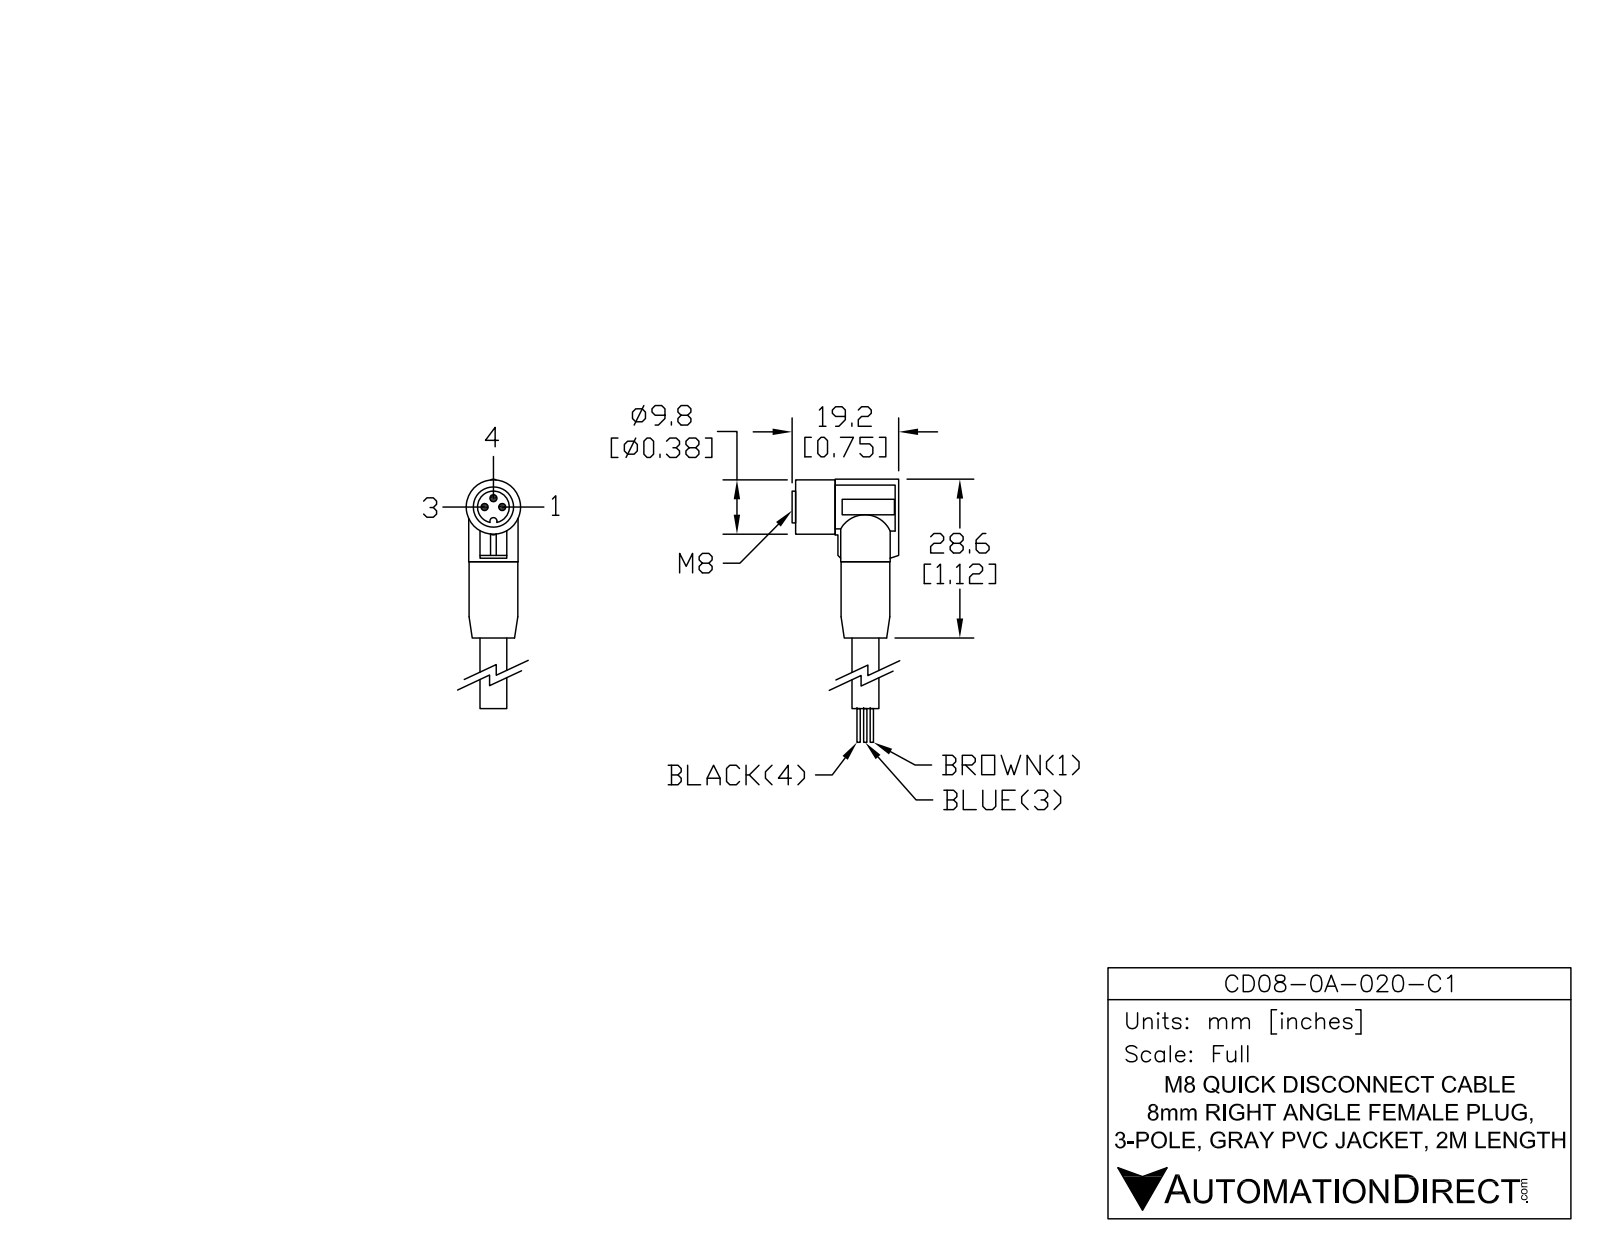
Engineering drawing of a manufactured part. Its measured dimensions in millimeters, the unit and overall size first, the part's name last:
Units: millimetres
Overall size (bounding box): 128.6 × 19.1 × 10
Round holes (diameter × count): ⌀0.9 ×3, ⌀5.6 ×1, ⌀8 ×1
Round bosses / shafts (diameter × count): ⌀10 ×2, ⌀6.6 ×1, ⌀5.5 ×1, ⌀4.8 ×1
Partial cylindrical surfaces — rounded edges, fillets, slot ends (radius × count): R0.5 ×1, R4.9 ×1
Main face-to-face distances: 9, 0.6, 4.6, 3.1, 4, 7.1, 7.7, 100, 2.5, 5.2
Hole centre spacings: 1.6, 2.26, 3.2
Volume: 4 277 mm³ · Surface area: 3 298 mm²
Bodies: 4 solids, 307 faces (222 planar, 82 cylindrical, 3 other)
Part name (STEP PRODUCT): CD08-0A-020-C1
STEP written by: SolidWorks 2017 (AUTOMOTIVE_DESIGN)
